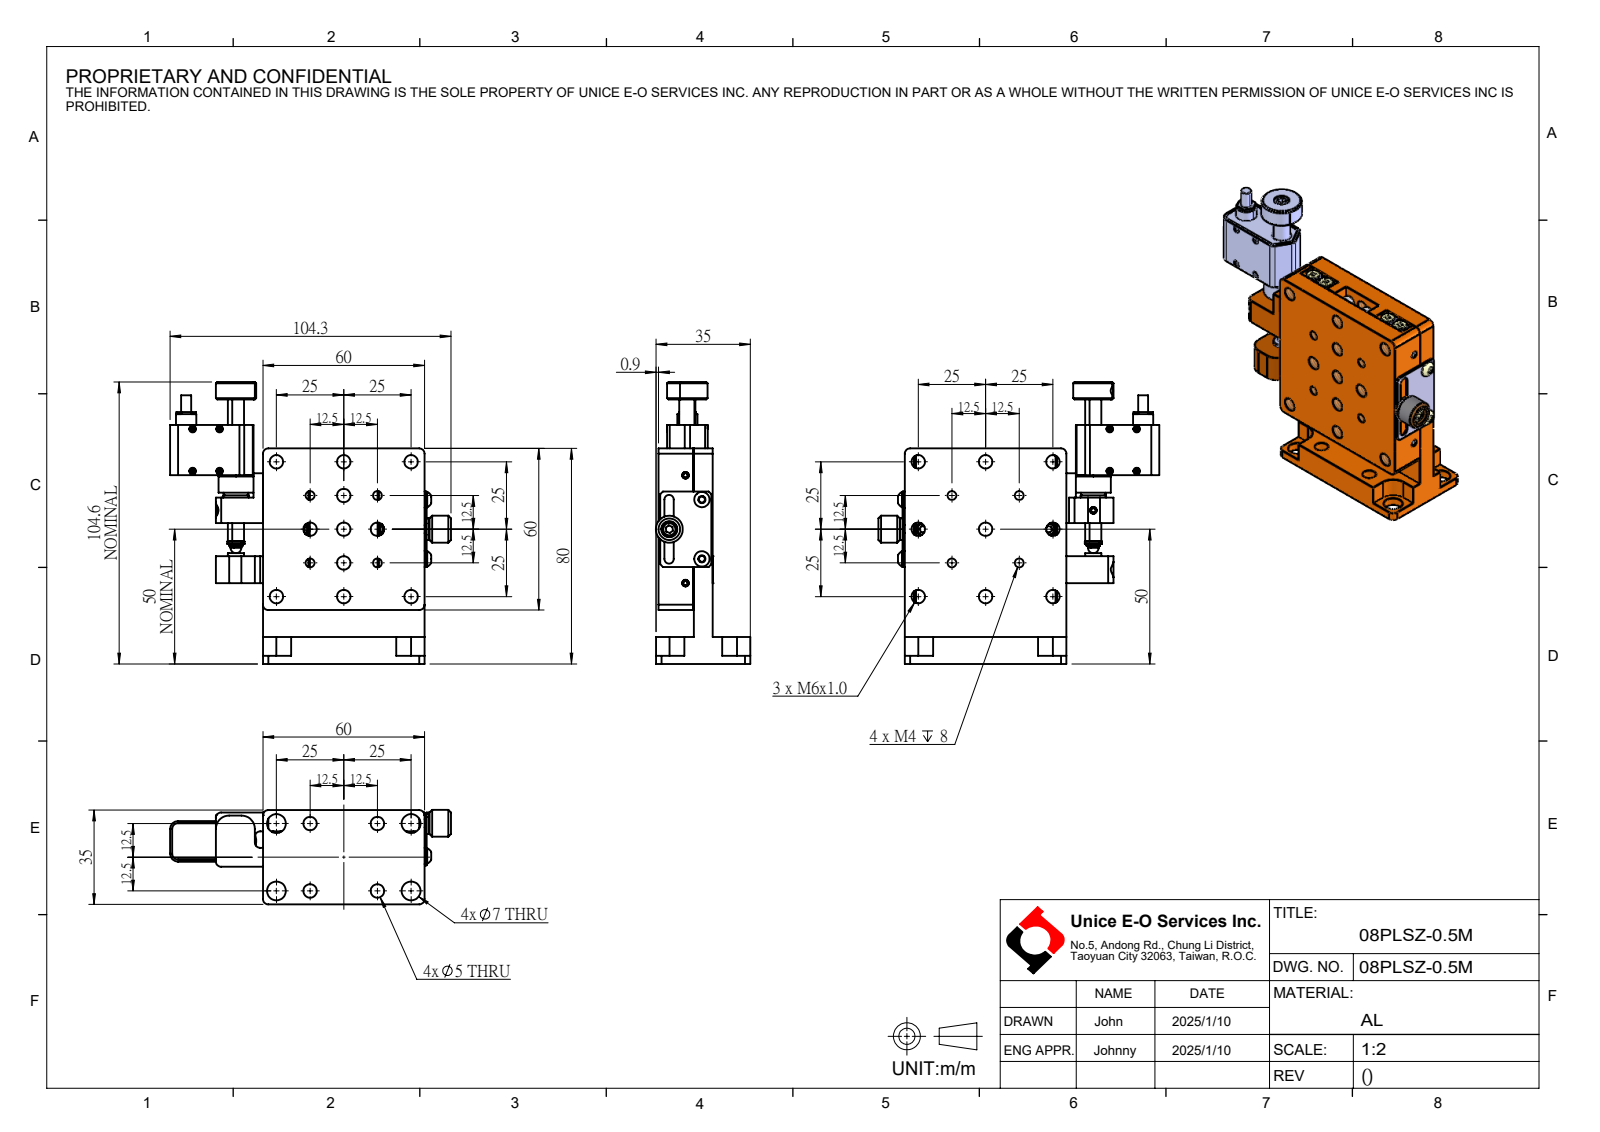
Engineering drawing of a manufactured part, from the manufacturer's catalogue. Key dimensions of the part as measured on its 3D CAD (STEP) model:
Part name (STEP PRODUCT): 08PLSZ-0.5M
STEP written by: SolidWorks 2024 (CONFIG_CONTROL_DESIGN)
Units: millimetres
Bodies: 0 solids, 1515 faces (767 planar, 459 cylindrical, 289 other)
Overall size (bounding box): 104.6 × 104.3 × 35.1
Round holes (diameter × count): ⌀5 ×30, ⌀2.05 ×20, ⌀2.5 ×16, ⌀3 ×13, ⌀3.3 ×4, ⌀7 ×4, ⌀3.4 ×3, ⌀6.5 ×3, ⌀1.4 ×2, ⌀2 ×2, ⌀3.2 ×2, ⌀3.5 ×2
Round bosses / shafts (diameter × count): ⌀4.5 ×16, ⌀2.5 ×16, ⌀3 ×9, ⌀5.5 ×4, ⌀5 ×4, ⌀2.55 ×4, ⌀6 ×3, ⌀5.7 ×2
Partial cylindrical surfaces — rounded edges, fillets, slot ends (radius × count): R2 ×15, R5 ×4, R5.5 ×4, R1.75 ×2, R3 ×2, R2.5 ×1
Main face-to-face distances: 7, 13.1, 6.1, 20.1, 6.9, 6, 10, 6.2, 13.2, 7.1
Hole centre spacings: 25, 17.68, 39.53, 20, 35.36, 27.95, 55.9, 10
